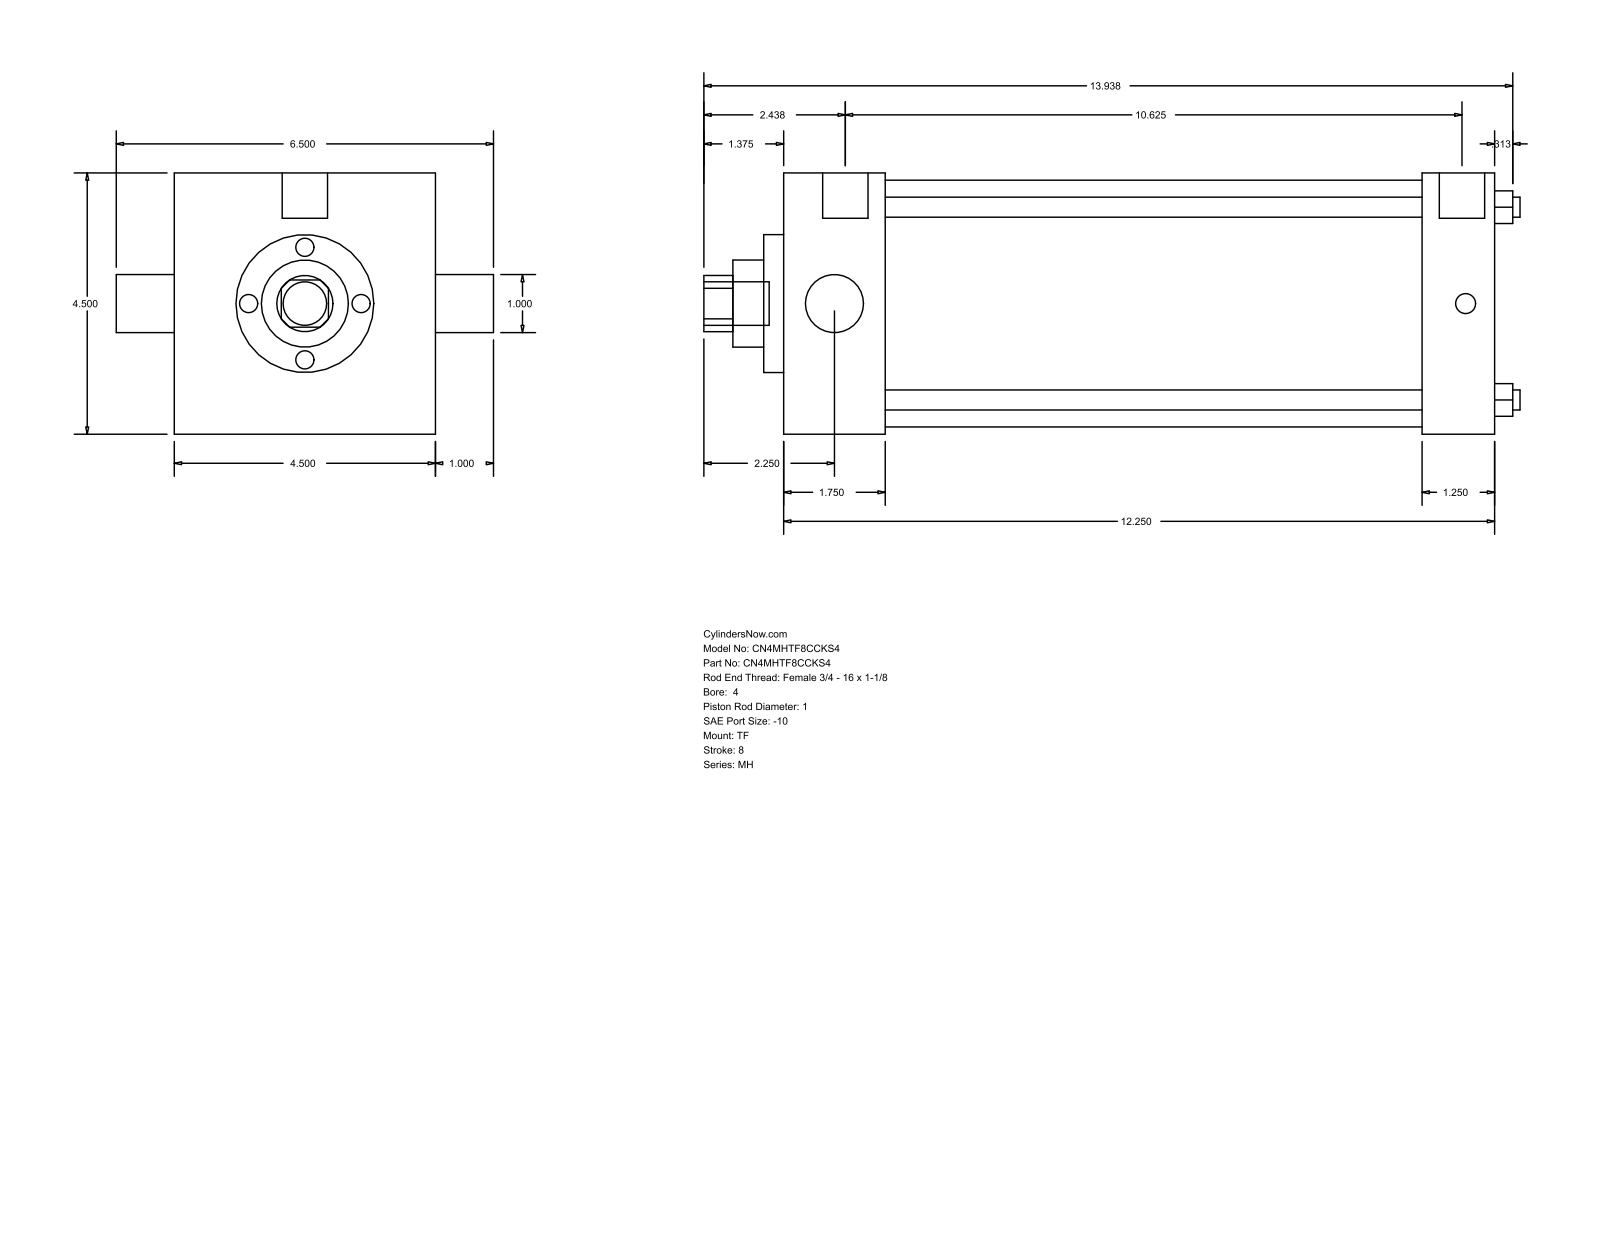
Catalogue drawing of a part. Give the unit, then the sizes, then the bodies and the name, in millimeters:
Units: millimetres
Overall size (bounding box): 357.19 × 165.1 × 114.3
Round holes (diameter × count): ⌀8.76 ×4, ⌀25.4 ×2, ⌀38.1 ×1, ⌀60.33 ×1, ⌀107.95 ×1
Round bosses / shafts (diameter × count): ⌀8.73 ×3, ⌀19.84 ×2, ⌀19.05 ×1
Partial cylindrical surfaces — rounded edges, fillets, slot ends (radius × count): R12.29 ×1
Main face-to-face distances: 114.3, 311.15, 44.46, 266.69, 279.4, 234.94, 31.75, 8.73, 53.19, 288.13
Hole centre spacings: 59.62, 84.32, 119.25
Bodies: 0 solids, 86 faces (61 planar, 25 cylindrical, 0 other)
Part name (STEP PRODUCT): MH_TF__0400_1
STEP written by: GSSL Pune (CONFIG_CONTROL_DESIGN)
